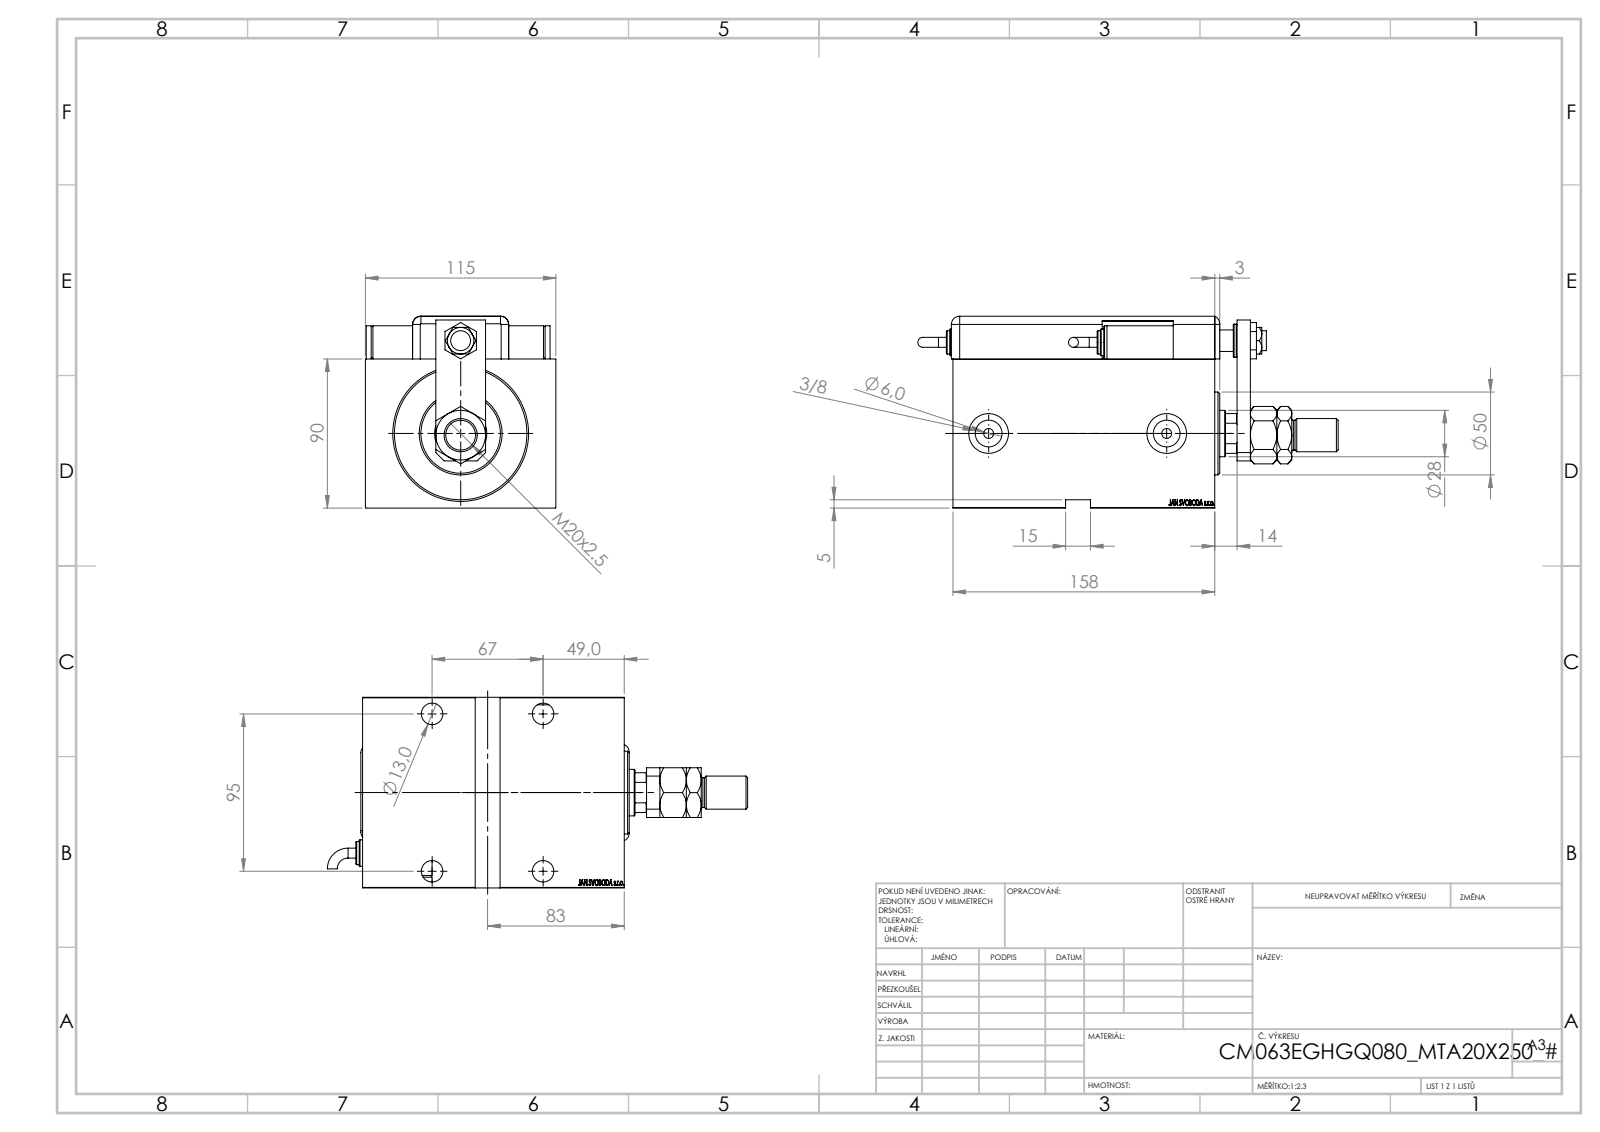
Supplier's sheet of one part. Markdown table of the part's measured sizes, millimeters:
| quantity | value |
| --- | --- |
| part name | V450CM_E_Body; NUT_D13; KRYT; SWITCH_Q_FRONT_BACK (+7 more) |
| STEP written by | SolidWorks 2019 (CONFIG_CONTROL_DESIGN) |
| units | millimeters |
| bodies | 14 solids, 1292 faces (632 planar, 113 cylindrical, 547 other) |
| overall size | 253.76 × 115.8 × 115 |
| volume | 1 527 000 mm³ |
| surface area | 246 618 mm² |
| round holes (diameter × count) | 13 × 5, 19 × 4, 4 × 2, 6 × 2, 8 × 2, 16.17 × 2, 24 × 2, 12 × 1, 14 × 1, 18.5 × 1, 20 × 1, 28 × 1 |
| round bosses / shafts (diameter × count) | 20 × 3, 16 × 2, 14 × 2, 6 × 2, 50 × 1, 18 × 1 |
| partial cylindrical surfaces (radius × count) | 5 × 9, 10 × 1, 13.5 × 1 |
| main face-to-face distances | 90, 3, 115, 158, 115.8, 25.8, 17.5, 140.5, 28.5, 22.8 |
| hole center spacings | 55.93, 67, 70.91, 95, 114.8, 116.25, 122.79, 1 |
